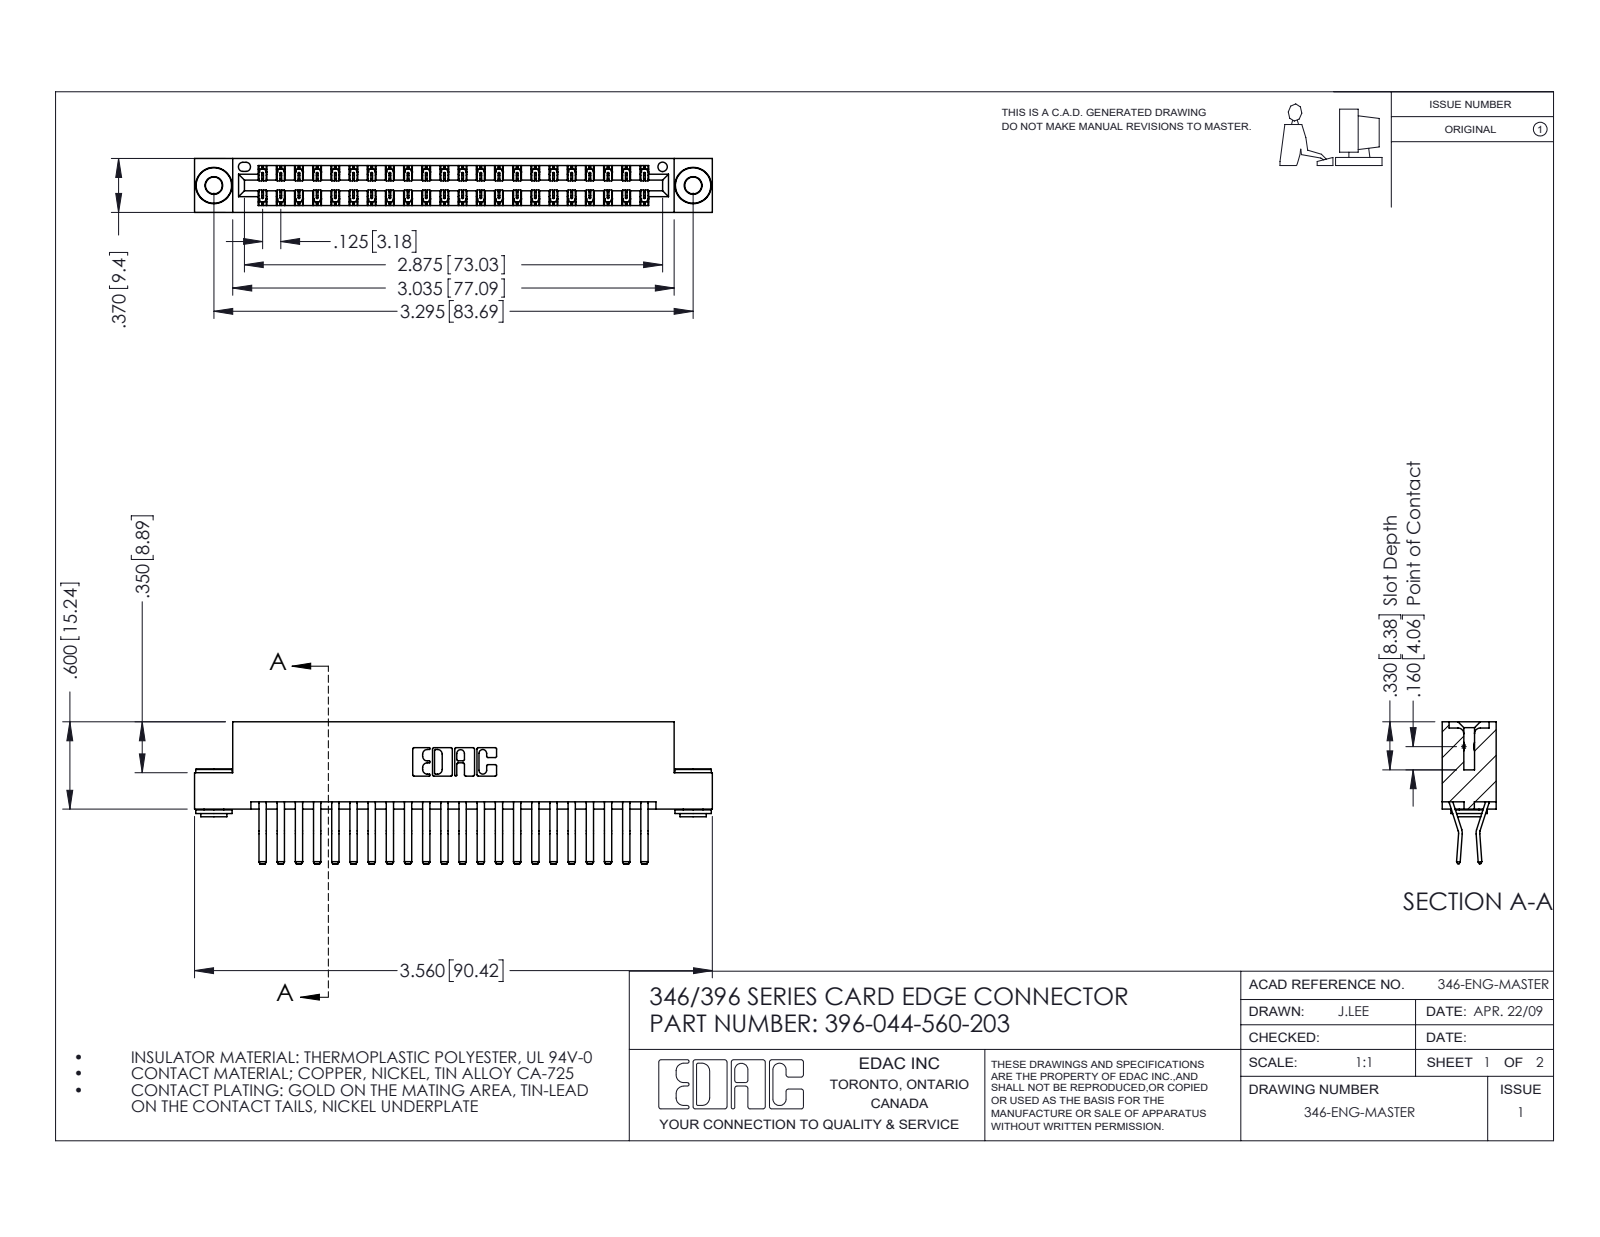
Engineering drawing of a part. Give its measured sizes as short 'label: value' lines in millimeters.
name: 345-250-002_345-250-002-102; 396-044-560-203; 345-292-001_560 Tail; 346 Part_Flush Mounting Lugs - 0.156 Dia-TH
written by: SolidWorks 2016 (CONFIG_CONTROL_DESIGN)
unit: mm
bodies: 47 solids, 2536 faces (1626 planar, 902 cylindrical, 8 other)
size: 90.4 × 24.8 × 9.4
volume: 8 960 mm³; area: 13 000 mm²
holes: 2× ⌀2.9, 2× ⌀4, 1× ⌀1.6
bosses: 2× ⌀6.4, 2× ⌀4.6, 2× ⌀3.5
rounds: 66× R0.2, 22× R0.3, 6× R0.2, 6× R0.8, 3× R0.7, 2× R0.3, 2× R0.4, 2× R0.6
face distances: 1.2, 8.2, 6.4, 9.4, 0.6, 1.8, 7.6, 7, 3.8, 5.6
hole spacings: 6.2, 78.4, 83.7
